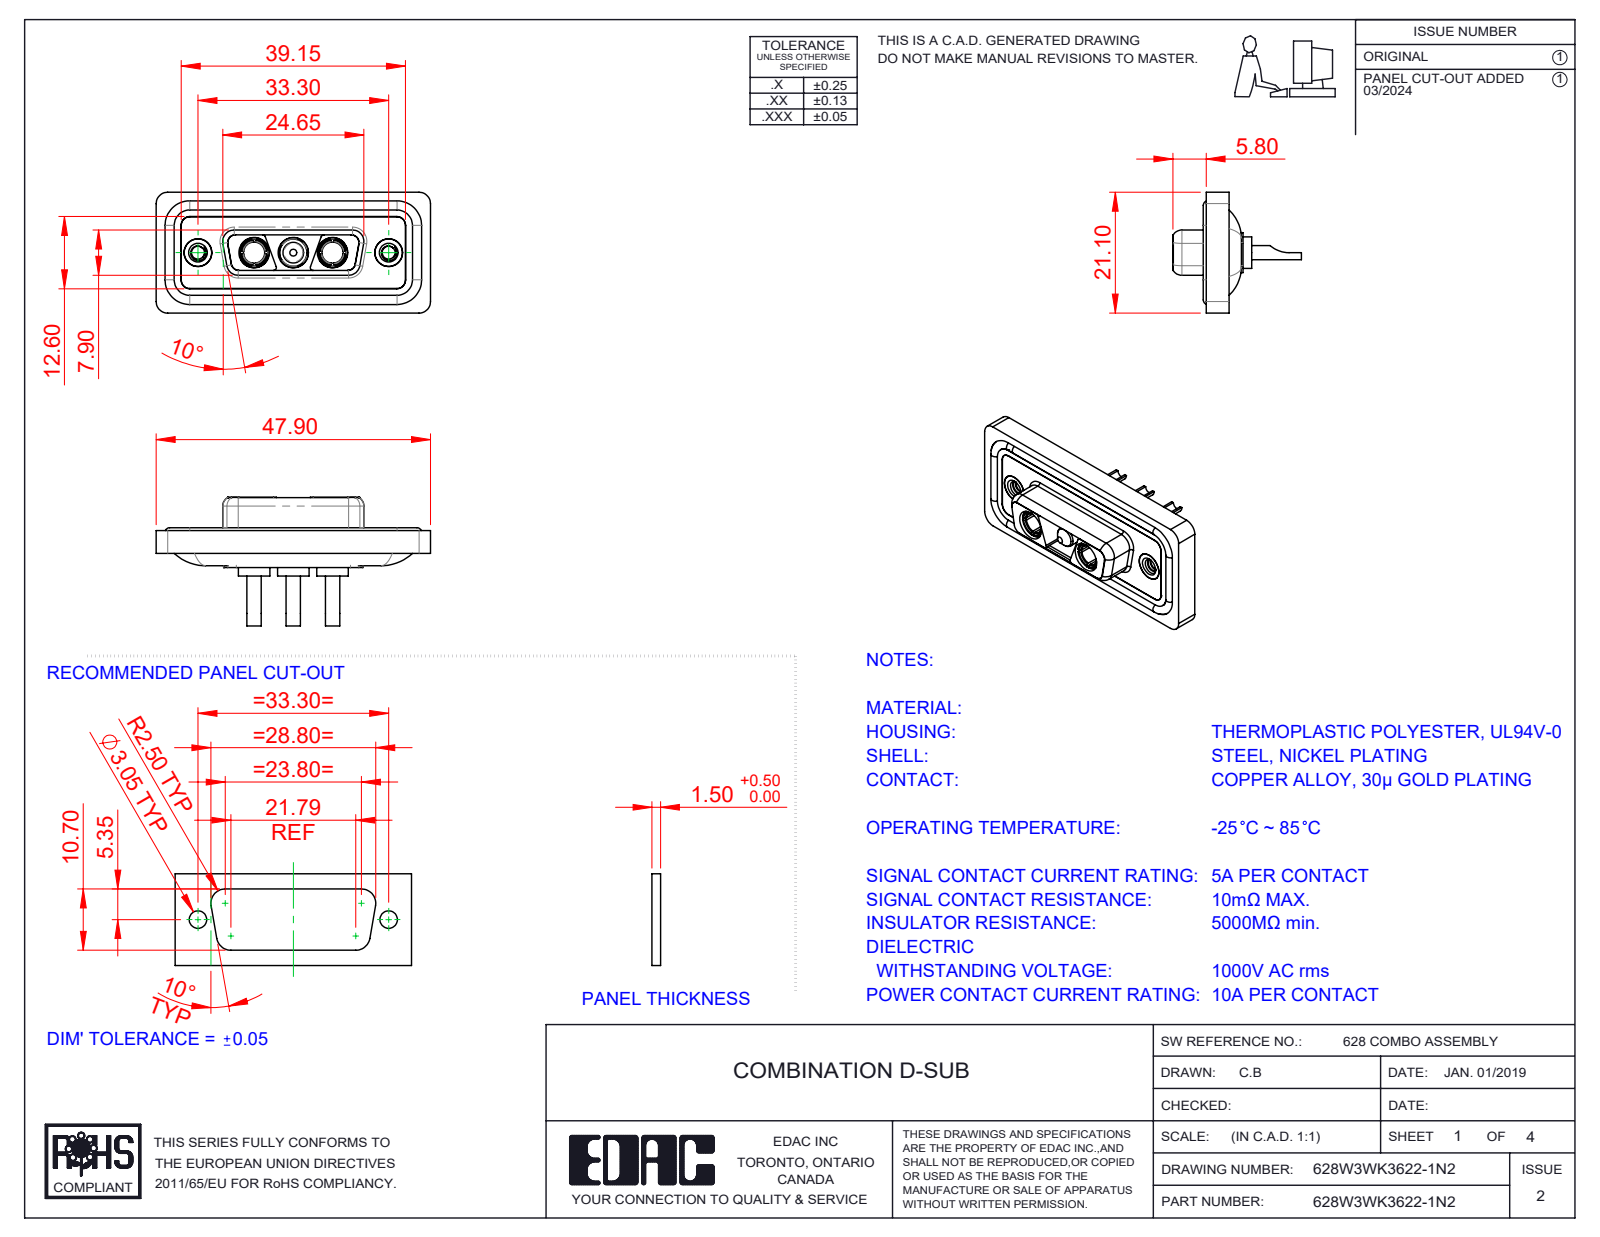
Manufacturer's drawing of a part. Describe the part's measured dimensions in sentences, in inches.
The part is named "628Combo Shell Rear_15 Contacts; 628Combo Housing_3WK3; 628Combo Shell Front_15 Contacts; 628Combo Waterproof Housing_15 Contacts (+4 more)". Its 3-D file was written by "SolidWorks 2023 (CONFIG_CONTROL_DESIGN)". It is 13 solids with 599 faces: 184 planar, 267 cylindrical and 148 other. Overall it measures 1.886 by 0.884 by 0.831 inches. Its volume is 0.358 cubic inches and its surface area 14.95 square inches. Round holes: 5 of diameter 0.191, 3 of diameter 0.067, 3 of diameter 0.209, 2 of diameter 0.089, 2 of diameter 0.146, 2 of diameter 0.157, 2 of diameter 0.159, 2 of diameter 0.197. Round bosses or shafts: 4 of diameter 0.063, 3 of diameter 0.217, 3 of diameter 0.205, 3 of diameter 0.187, 3 of diameter 0.148, 3 of diameter 0.098, 2 of diameter 0.195, 2 of diameter 0.195. Partial cylindrical surfaces (rounded edges, fillets, slot ends): 22 of radius 0.059, 20 of radius 0.079, 12 of radius 0.053, 8 of radius 0.02, 8 of radius 0.063, 4 of radius 0.01, 4 of radius 0.024, 4 of radius 0.026. The main face-to-face distances are 0.016, 0.063, 0.071, 0.02, 0.043, 0.114, 0.222, 0.278, 0.059, 0.211. The hole center spacings are 0.27, 0.386, 0.656, 0.925, 0.539, 1.311.
